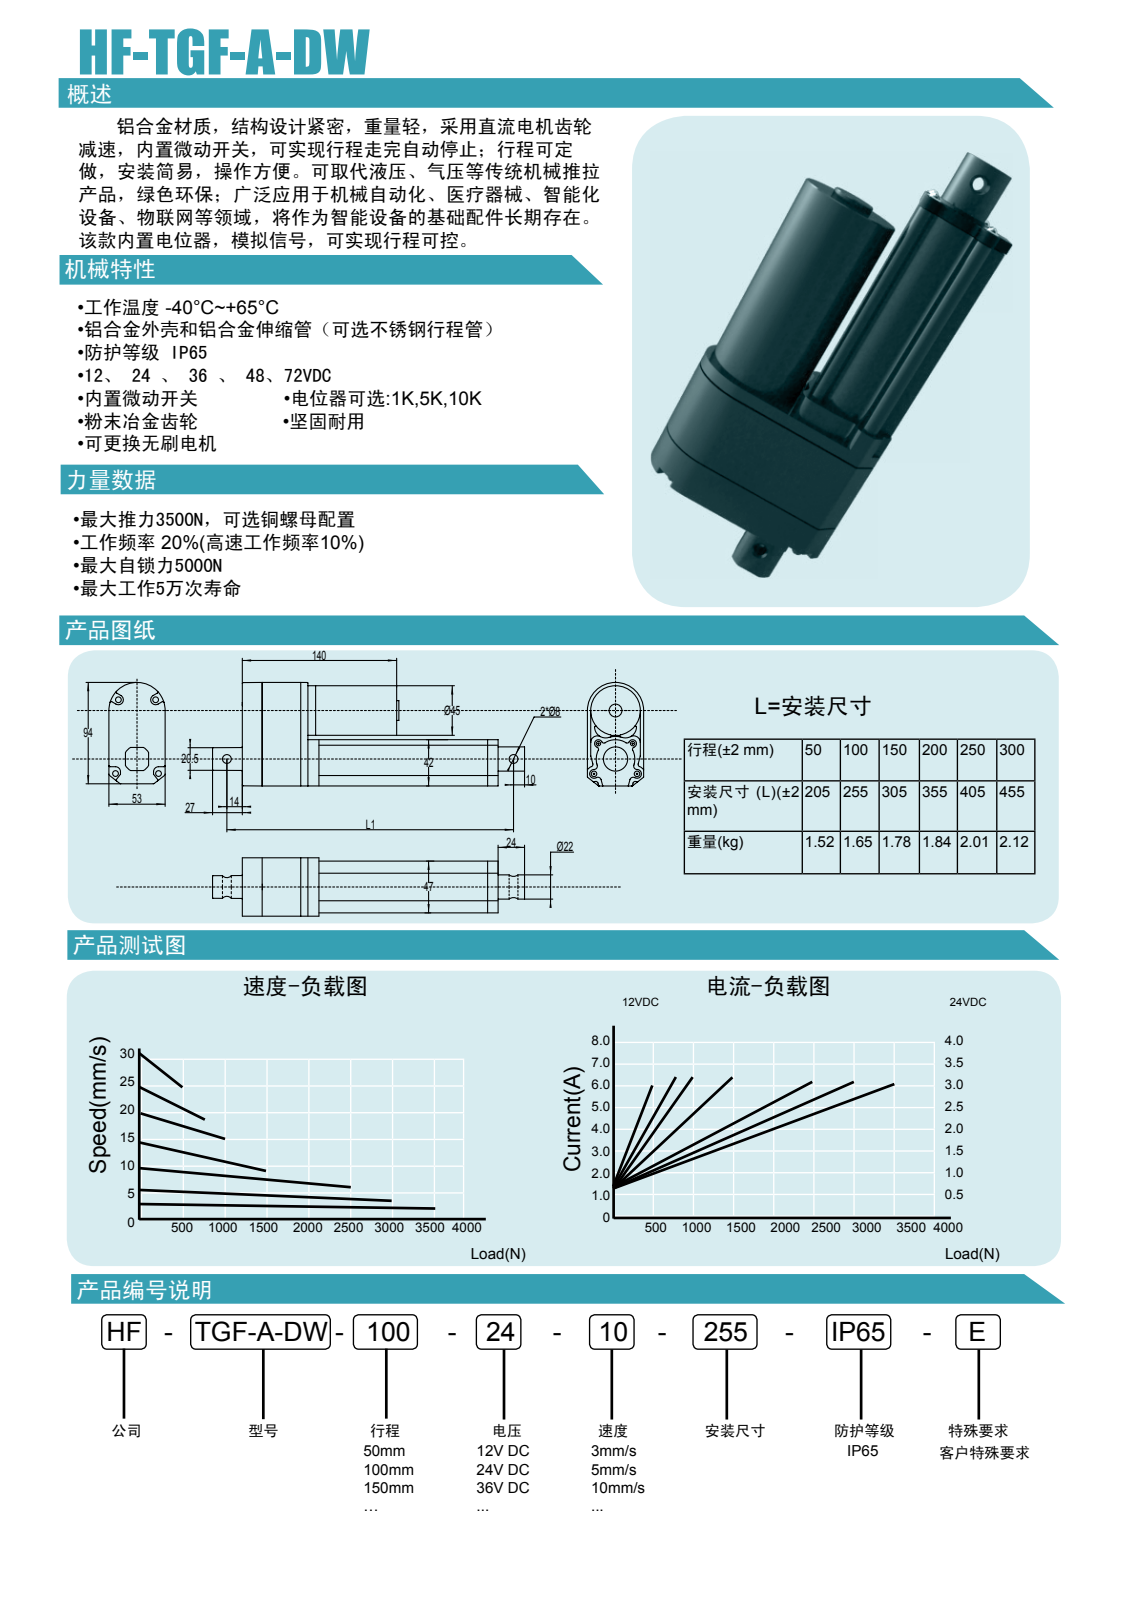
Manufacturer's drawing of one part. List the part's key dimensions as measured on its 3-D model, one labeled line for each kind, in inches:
Part name (STEP PRODUCT): DOWN; UP; MOTER; WAIKE (+4 more)
STEP written by: PRO/ENGINEER BY PARAMETRIC TECHNOLOGY CORPORATION, 2008380 (CONFIG_CONTROL_DESIGN)
Units: inches
Bodies: 7 solids, 313 faces (80 planar, 108 cylindrical, 125 other)
Overall size (bounding box): 10.906 × 3.72 × 2.008
Volume: 32.68 in³ · Surface area: 208.1 in²
Round holes (diameter × count): ⌀0.323 ×2, ⌀0.394 ×1, ⌀0.866 ×1
Round bosses / shafts (diameter × count): ⌀1.772 ×1, ⌀0.748 ×1
Partial cylindrical surfaces — rounded edges, fillets, slot ends (radius × count): R0.02 ×29, R0.079 ×10, R0.039 ×8, R0.059 ×8, R0.118 ×4, R0.177 ×4, R0.138 ×2, R0.157 ×2
Main face-to-face distances: 1.368, 1.378, 1.358, 2.008, 0.709, 0.719, 2.077, 2.087, 0.256, 2.343
Hole centre spacings: 10.039
